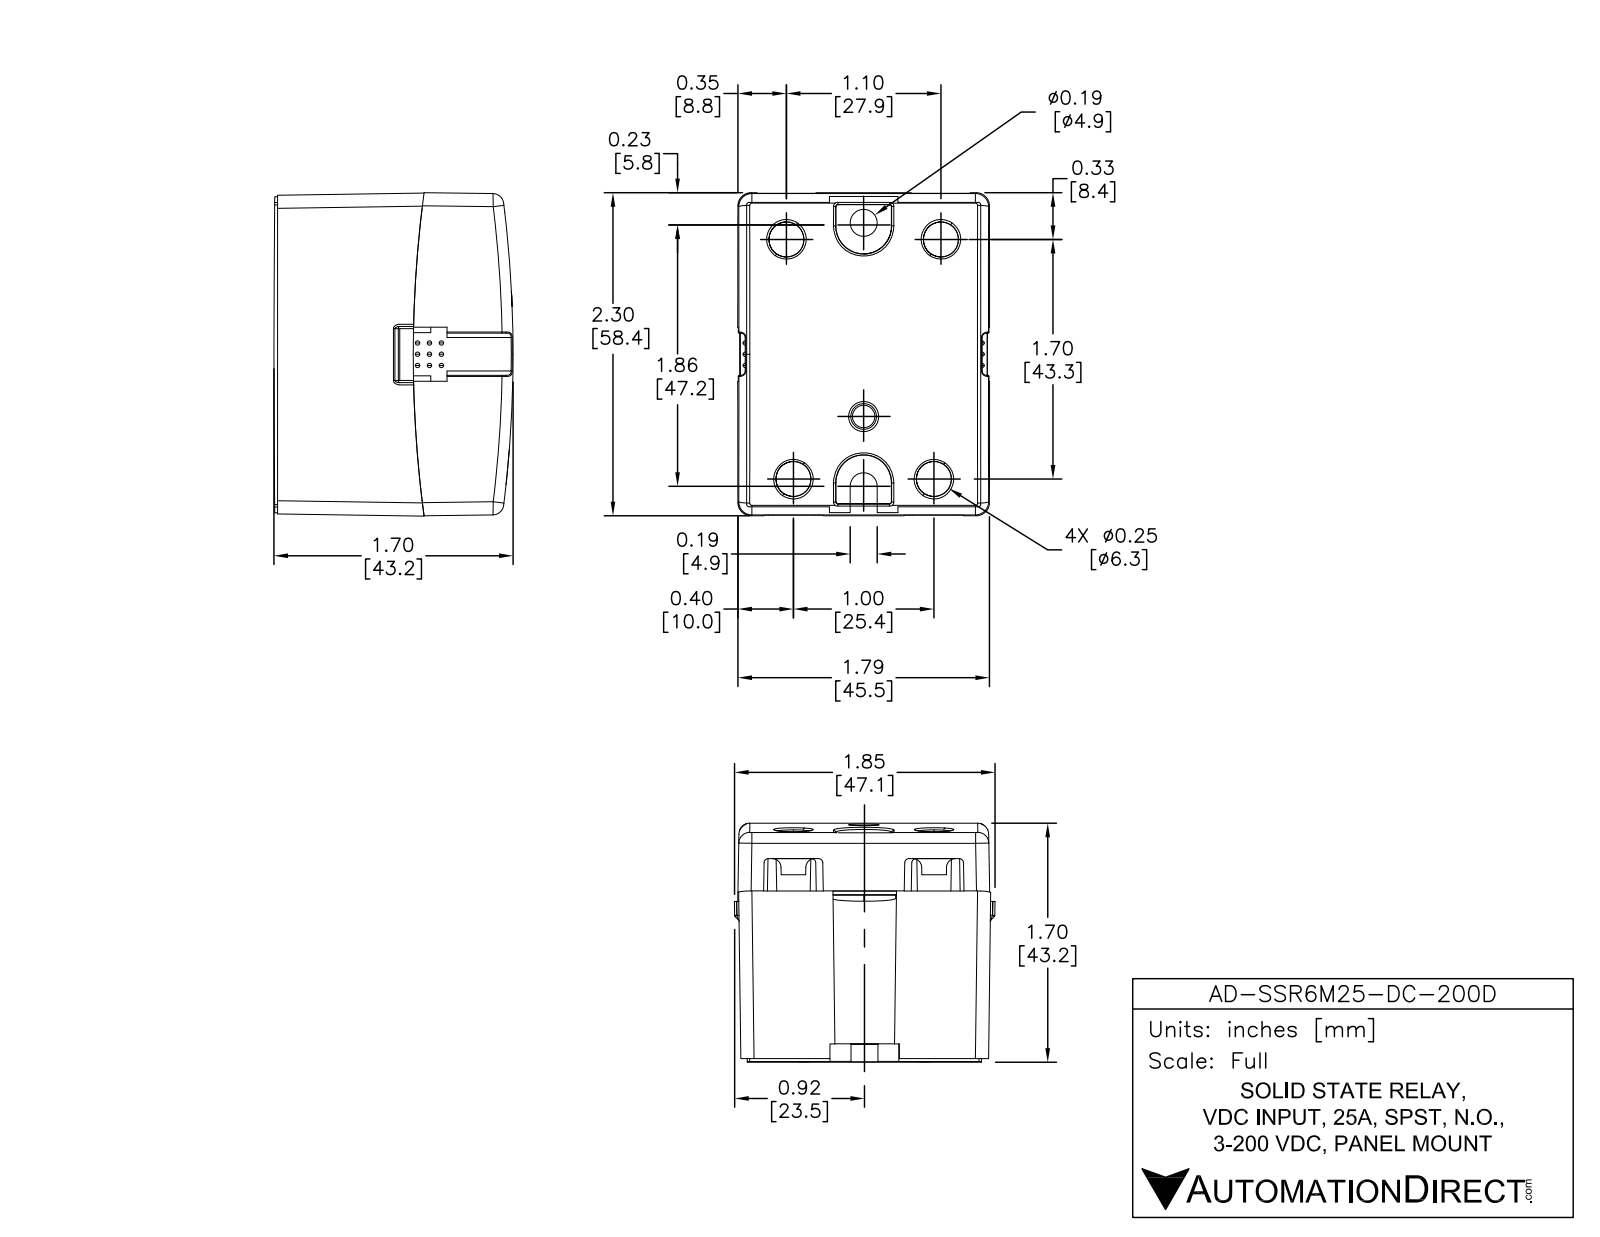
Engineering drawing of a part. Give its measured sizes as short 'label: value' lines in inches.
name: AD-SSR6M25-DC-200D
written by: SolidWorks 2013 (AUTOMOTIVE_DESIGN)
unit: in
bodies: 1 solid, 330 faces (196 planar, 111 cylindrical, 23 other)
size: 2.3 × 1.79 × 1.7
volume: 6.262 in³; area: 30.25 in²
holes: 4× ⌀0.25, 1× ⌀0.19
bosses: 2× ⌀0.4, 2× ⌀0.35, 2× ⌀0.306, 2× ⌀0.3, 2× ⌀0.2, 2× ⌀0.2
rounds: 6× R0.03, 4× R0.01, 2× R0.04, 2× R0.194, 1× R0.095, 1× R0.498, 1× R0.5, 1× R0.528
face distances: 1.79, 2.3, 1.3, 1.05, 0.25, 0.05, 0.671, 1.059, 0.075, 2.225
hole spacings: 1.1, 1.7, 2.025, 0.554, 0.564, 1.881, 1.883
